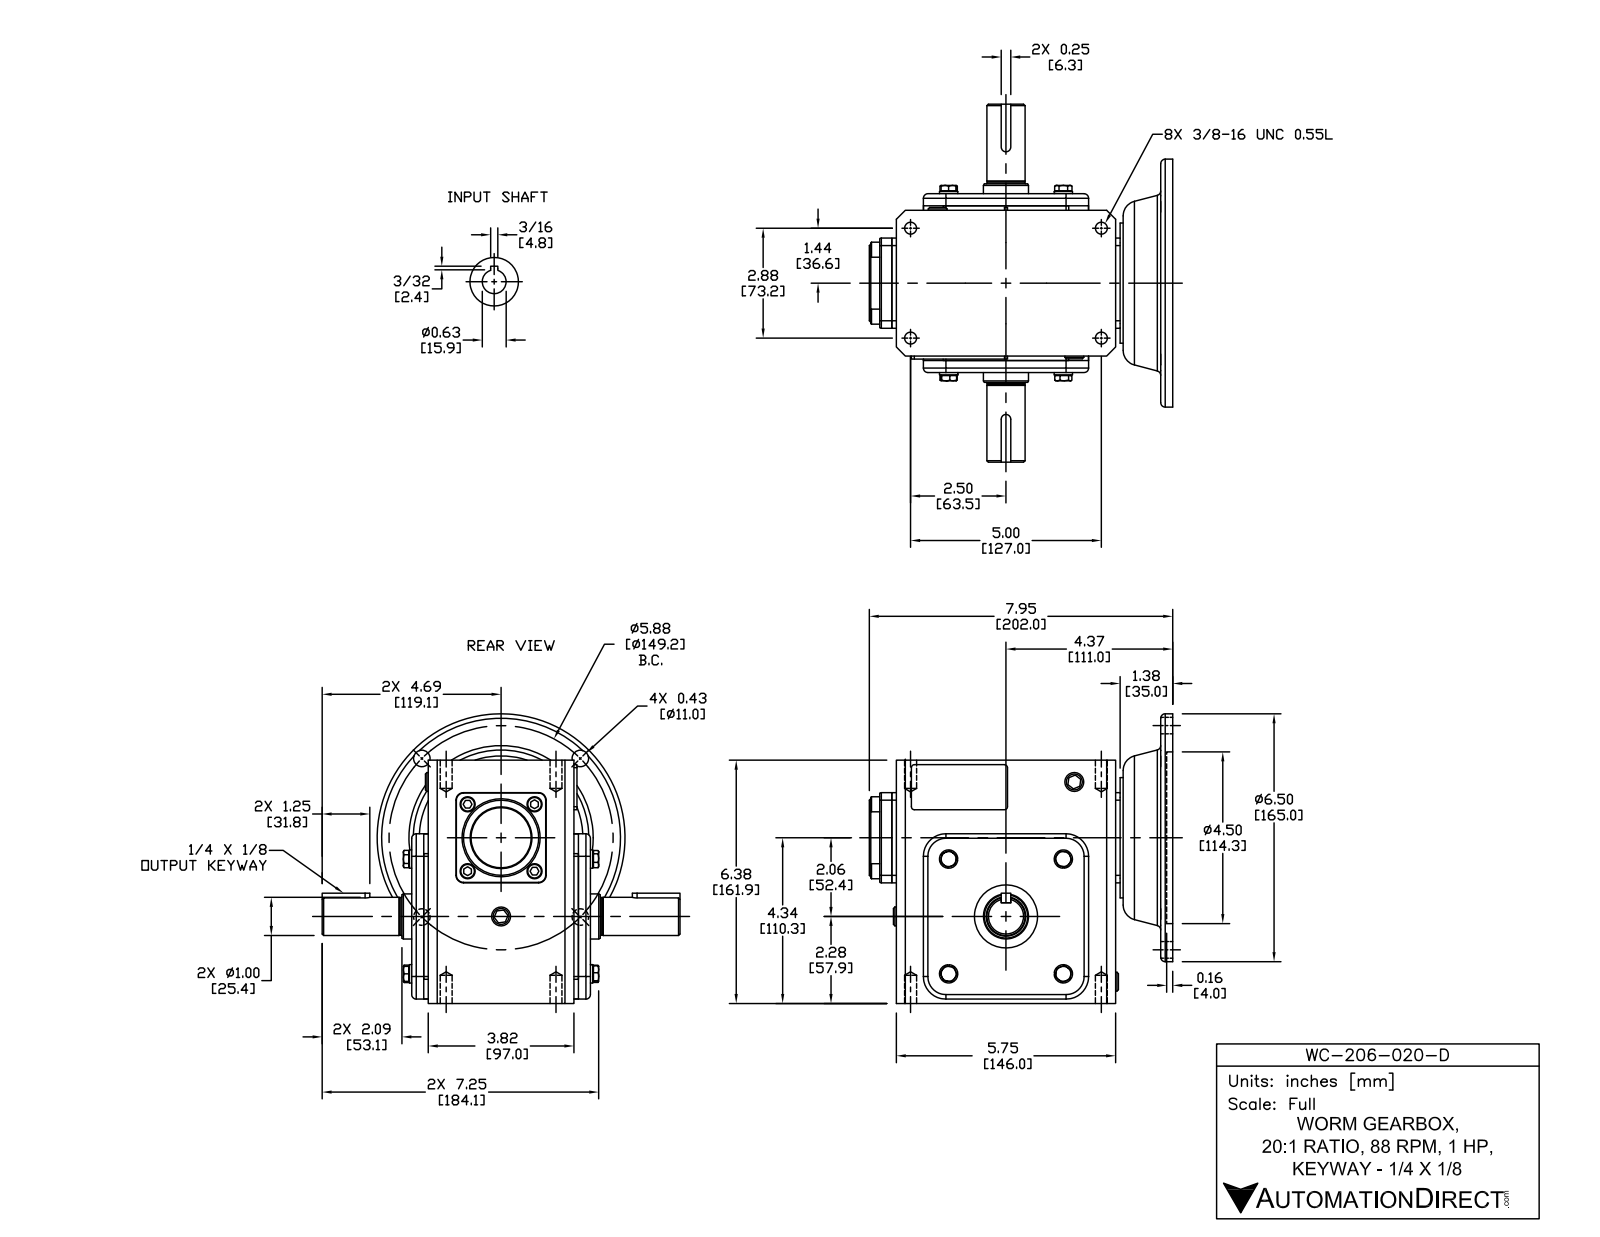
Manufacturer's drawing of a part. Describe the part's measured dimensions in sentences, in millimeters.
The part is named "WG-206-020-D". Its 3-D file was written by "SolidWorks 2015 (CONFIG_CONTROL_DESIGN)". It is 45 solids with 639 faces: 311 planar, 194 cylindrical and 134 other. Overall it measures 238.3 by 202 by 192.8 millimeters. Its volume is 2 863 000 cubic millimeters and its surface area 272 800 square millimeters. Round holes: 4 of diameter 8, 4 of diameter 10.3, 1 of diameter 15, 1 of diameter 15.9, 1 of diameter 30, 1 of diameter 37, 1 of diameter 42, 1 of diameter 90, 1 of diameter 114.3. Round bosses or shafts: 8 of diameter 10, 4 of diameter 12.2, 1 of diameter 165, 1 of diameter 80, 1 of diameter 52, 1 of diameter 40, 1 of diameter 30, 1 of diameter 29. Partial cylindrical surfaces (rounded edges, fillets, slot ends): 8 of radius 2, 8 of radius 3, 4 of radius 5, 4 of radius 15, 2 of radius 0.5, 2 of radius 1, 2 of radius 3.2, 1 of radius 69. The main face-to-face distances are 8, 3, 103, 11, 111, 108, 100, 161.9, 119, 18. The hole center spacings are 74.6, 105.5, 52.8, 73.2, 117.6, 127, 146.6, 149.2.
